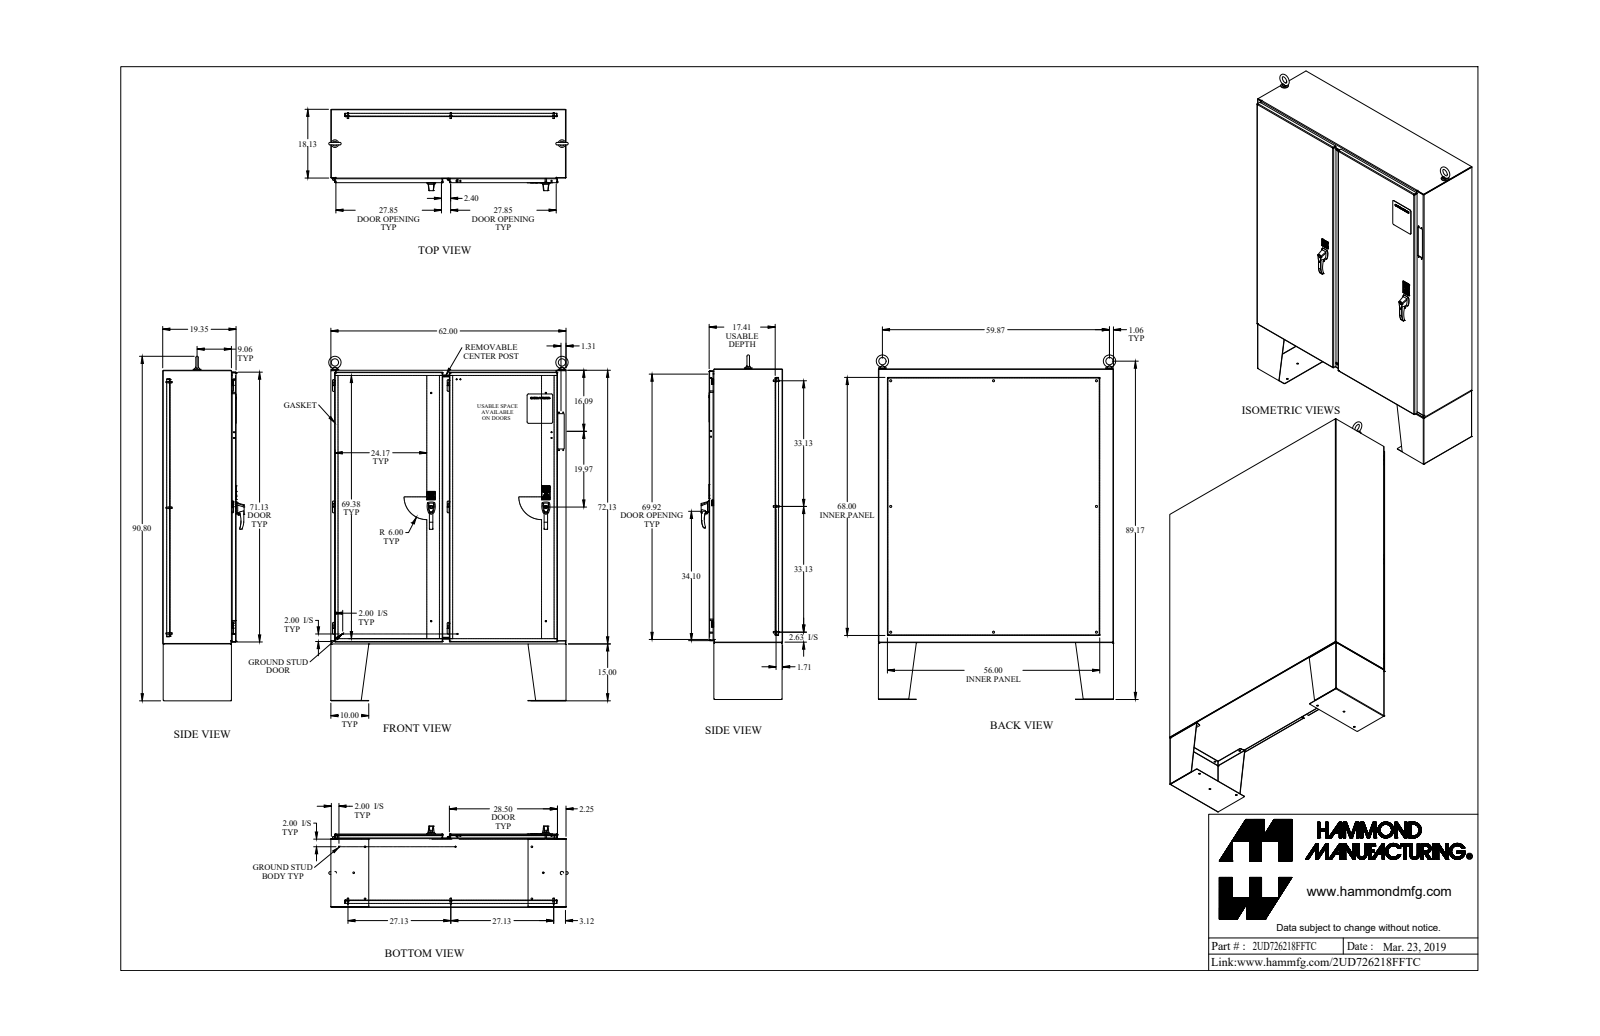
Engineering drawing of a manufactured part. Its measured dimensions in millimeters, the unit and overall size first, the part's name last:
Units: millimetres
Overall size (bounding box): 2306.3 × 1603.3 × 545.2
Round holes (diameter × count): ⌀11.1 ×14, ⌀7.1 ×11, ⌀7.8 ×11, ⌀5 ×10, ⌀6.4 ×10, ⌀8.9 ×8, ⌀6.5 ×6, ⌀8 ×6, ⌀11.3 ×5, ⌀7.1 ×4, ⌀7.2 ×4, ⌀9.5 ×4
Round bosses / shafts (diameter × count): ⌀6.4 ×19, ⌀25.4 ×14, ⌀16.5 ×9, ⌀9.5 ×9, ⌀8.4 ×9, ⌀7.1 ×8, ⌀19.1 ×6, ⌀13.5 ×6
Partial cylindrical surfaces — rounded edges, fillets, slot ends (radius × count): R3.2 ×62, R1.5 ×51, R12.7 ×38, R0.4 ×32, R4.7 ×30, R0.8 ×28, R1.2 ×20, R3.6 ×20
Main face-to-face distances: 3.2, 1.8, 442.7, 491.9, 488.8, 49.2, 46, 44.2, 47.4, 444.6
Hole centre spacings: 768.4, 190.2, 206.4, 220.3, 408.1, 768.9, 1206.5, 1324
Volume: 69 530 000 mm³ · Surface area: 29 550 000 mm²
Bodies: 214 solids, 3142 faces (1822 planar, 934 cylindrical, 386 other)
Part name (STEP PRODUCT): 2UD726218FFTC
STEP written by: SolidWorks 2018 (AUTOMOTIVE_DESIGN)
